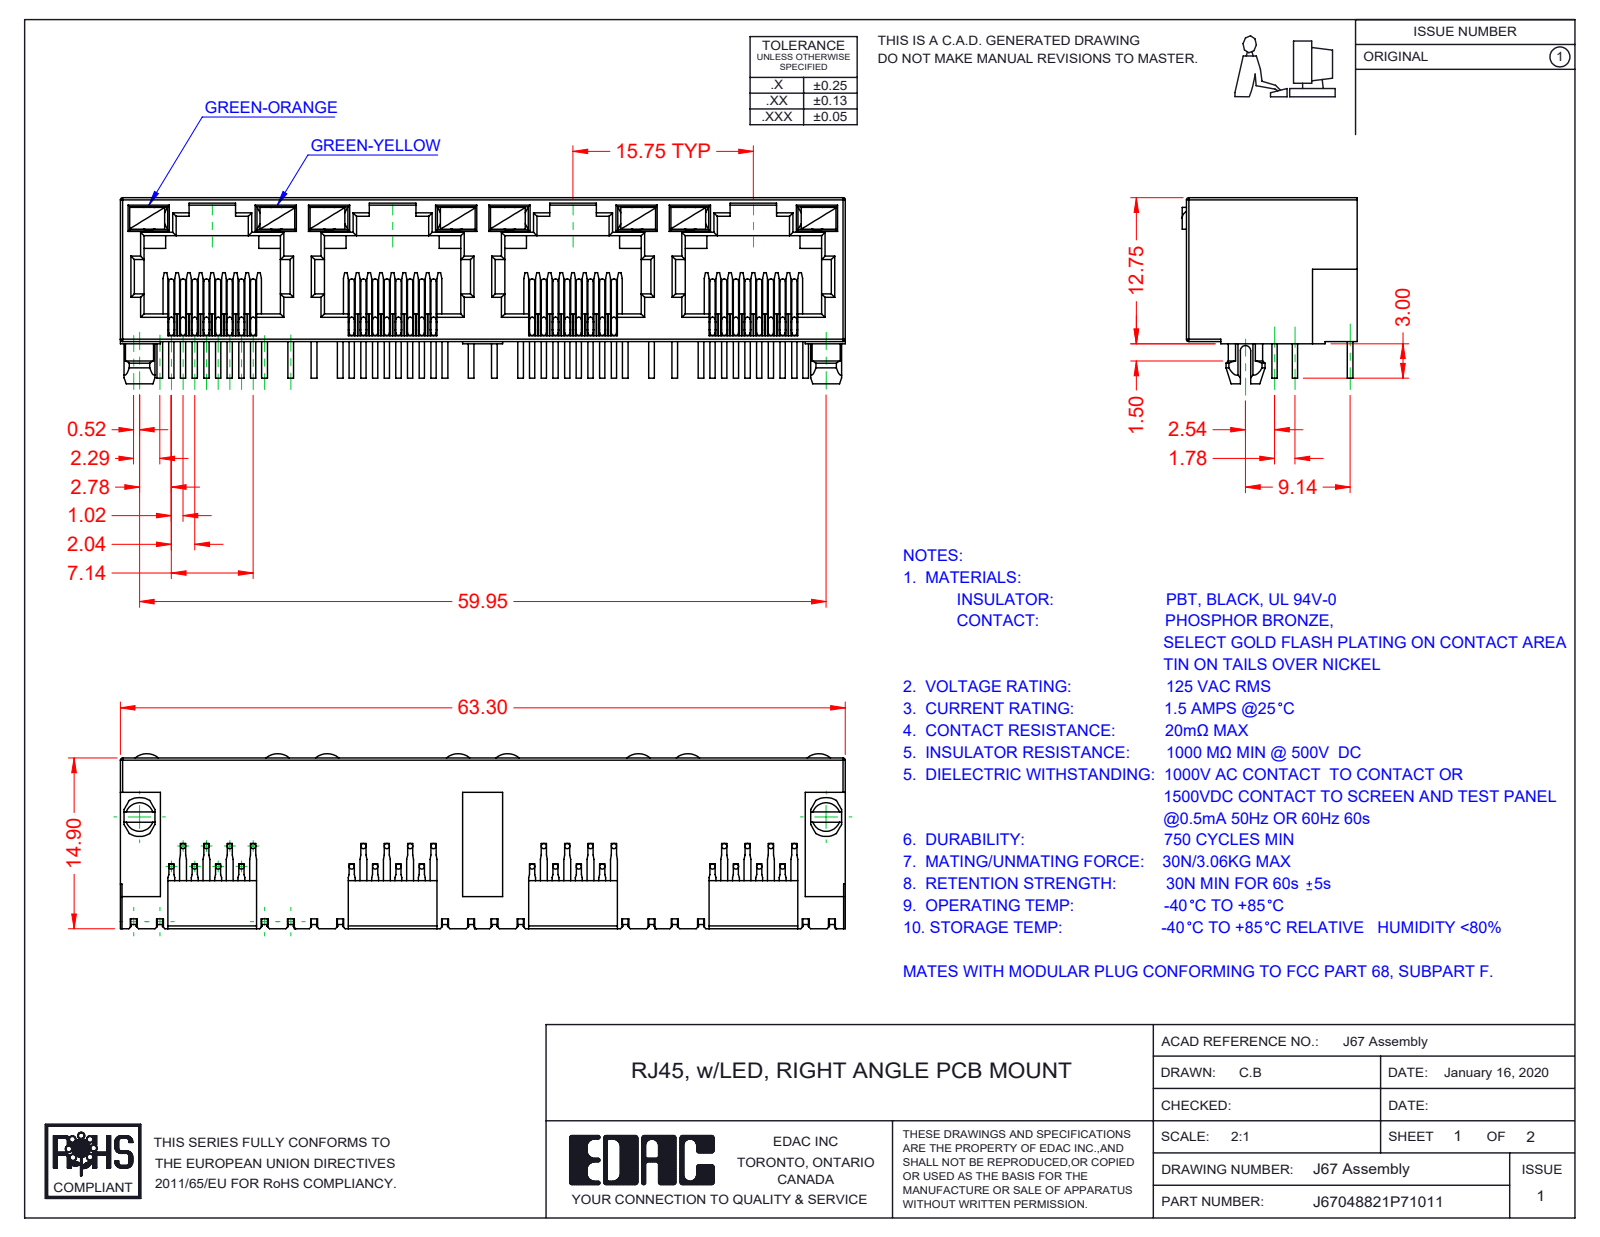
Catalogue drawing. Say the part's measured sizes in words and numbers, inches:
The part is named "67 LED RH_5-Green-Yellow; 67 LED LH_7-Green-Orange; 67 Contacts; 67 Insulator (+1 more)". Its 3-D file was written by "SolidWorks 2016 (CONFIG_CONTROL_DESIGN)". It is 41 solids with 2481 faces: 1781 planar, 492 cylindrical and 208 other. Overall it measures 2.492 by 0.64 by 0.602 inches. Its volume is 0.315 cubic inches and its surface area 17.94 square inches. Round bosses or shafts: 96 of diameter 0.018. Partial cylindrical surfaces (rounded edges, fillets, slot ends): 66 of radius 0.008, 29 of radius 0.012, 9 of radius 0.018, 8 of radius 0.061, 2 of radius 0.059, 2 of radius 0.067, 1 of radius 0.014, 1 of radius 0.039. The main face-to-face distances are 0.02, 0.494, 0.074, 0.035, 0.394, 0.62, 0.039, 0.055, 0.433, 0.468.
